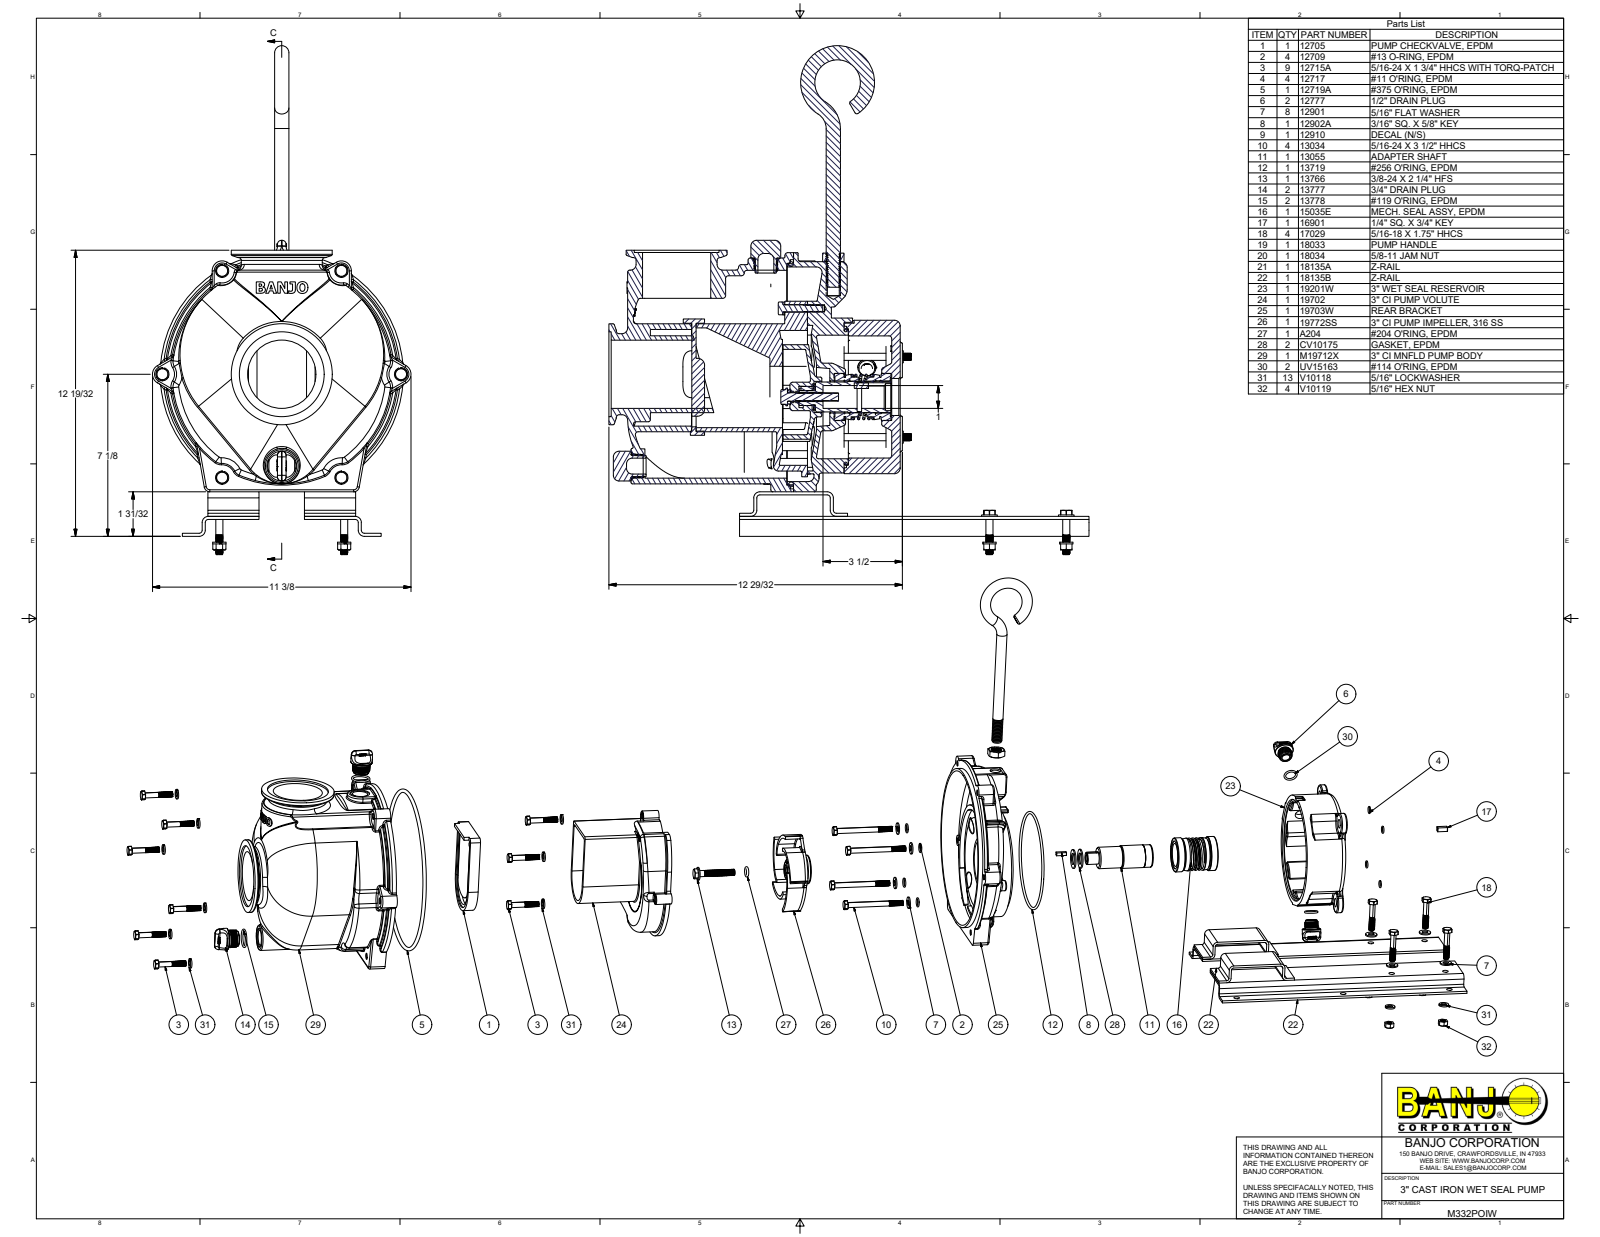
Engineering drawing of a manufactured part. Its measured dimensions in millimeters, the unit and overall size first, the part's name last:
Units: millimetres
Overall size (bounding box): 568.58 × 536.56 × 288.93
Round holes (diameter × count): ⌀8.73 ×14, ⌀8.18 ×13, ⌀6.78 ×9, ⌀8.2 ×9, ⌀23.81 ×5, ⌀6.41 ×4, ⌀7.95 ×4, ⌀8.13 ×4, ⌀10.79 ×4, ⌀13.49 ×4, ⌀14.25 ×4, ⌀13.92 ×3
Round bosses / shafts (diameter × count): ⌀7.02 ×260, ⌀6.82 ×60, ⌀7.94 ×17, ⌀14.81 ×13, ⌀17.48 ×8, ⌀9.68 ×4, ⌀15.88 ×3, ⌀112.78 ×2
Partial cylindrical surfaces — rounded edges, fillets, slot ends (radius × count): R1.52 ×126, R3.17 ×115, R2.29 ×96, R0.76 ×45, R3.51 ×26, R6.35 ×22, R12.7 ×19, R7.21 ×17
Main face-to-face distances: 3.42, 18.94, 27.43, 6.35, 46.37, 119.22, 30.85, 22.36, 9.53, 15.52
Hole centre spacings: 111.85, 133.35, 28.57, 89.81, 130.21, 155.58, 230.97, 63.51
Volume: 4 391 000 mm³ · Surface area: 1 421 000 mm²
Bodies: 82 solids, 7666 faces (1472 planar, 2565 cylindrical, 3629 other)
Part name (STEP PRODUCT): 19703W; 19201W; M19712X; 13719 (+8 more)
STEP written by: Autodesk Inventor 2014 (AUTOMOTIVE_DESIGN)
